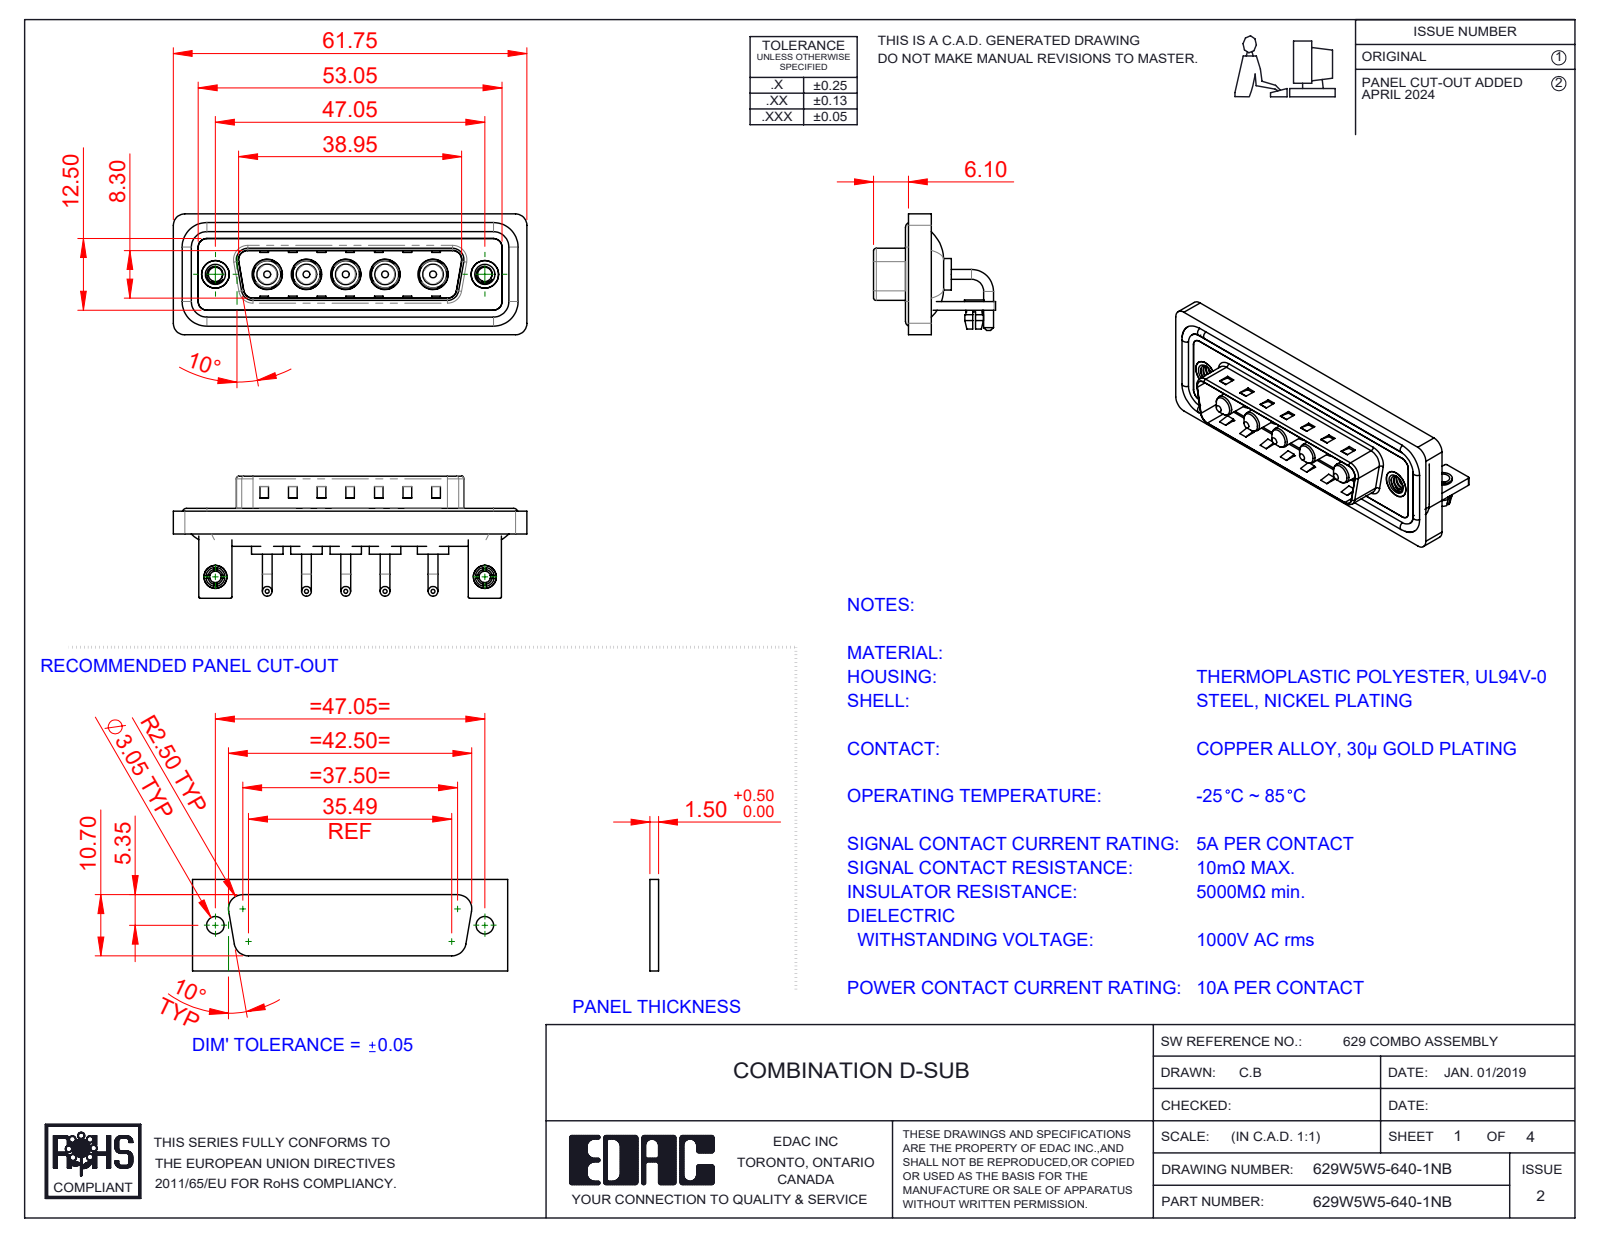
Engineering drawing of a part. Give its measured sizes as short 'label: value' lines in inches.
name: 629Combo Stabilizer Bracket; 629Combo Shell Front_25 Contacts; 629Combo Board Lock; 629Combo Housing_5W5 (+5 more)
written by: SolidWorks 2023 (CONFIG_CONTROL_DESIGN)
unit: in
bodies: 21 solids, 828 faces (327 planar, 343 cylindrical, 158 other)
size: 2.431 × 0.839 × 0.831
volume: 0.477 in³; area: 19.86 in²
holes: 5× ⌀0.191, 5× ⌀0.209, 4× ⌀0.098, 2× ⌀0.079, 2× ⌀0.126, 2× ⌀0.157, 2× ⌀0.189, 2× ⌀0.197
bosses: 10× ⌀0.067, 5× ⌀0.217, 5× ⌀0.205, 5× ⌀0.187, 5× ⌀0.148, 5× ⌀0.142, 4× ⌀0.063, 2× ⌀0.193
rounds: 19× R0.079, 18× R0.059, 16× R0.01, 9× R0.02, 8× R0.063, 5× R0.083, 4× R0.024, 4× R0.026
face distances: 0.016, 0.059, 0.114, 0.031, 0.083, 0.146, 0.043, 0.177, 0.161, 0.047
hole spacings: 0.27, 0.541, 1.852, 0.27, 0.27, 0.33, 0.33, 0.356
